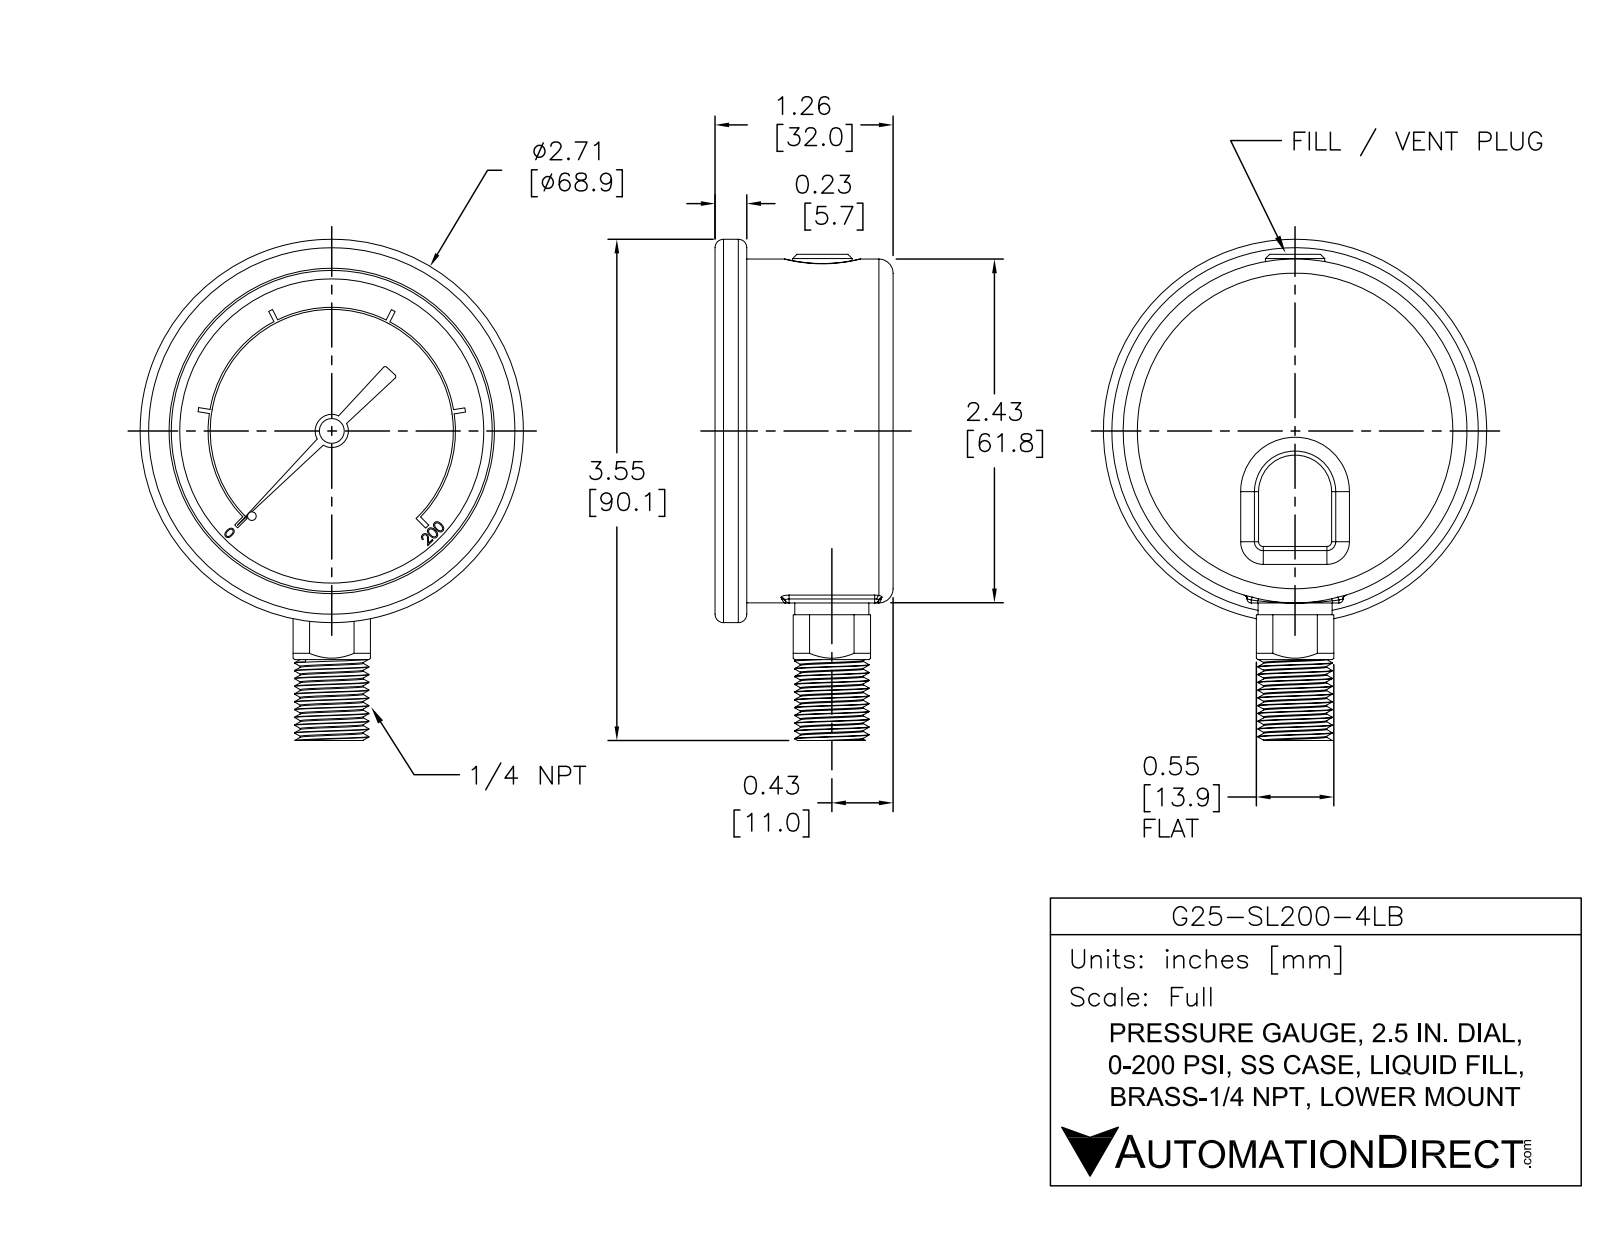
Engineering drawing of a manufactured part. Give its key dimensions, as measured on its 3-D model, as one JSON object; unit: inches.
{"part_name": "G25-SL200-4LB", "step_written_by": "SolidWorks 2021 (AUTOMOTIVE_DESIGN)", "units": "inches", "bodies": {"solids": 1, "faces": 349, "planar": 195, "cylindrical": 85, "other": 69}, "overall_size": [3.546, 2.713, 1.26], "volume_in3": 5.273, "surface_area_in2": 24.68, "round_holes": [[0.027, 1], [0.071, 1], [0.119, 1], [2.272, 1]], "round_bosses_or_shafts": [[2.713, 1], [2.433, 1], [0.524, 1], [0.42, 1], [0.235, 1], [0.176, 1], [0.14, 1], [0.041, 1]], "partial_cylinders_radius": [[0.03, 9], [0.1, 3], [0.015, 2], [0.316, 1], [0.86, 1], [0.875, 1]], "face_to_face_distances": [1.01, 1.26, 0.25, 1.035, 0.025, 0.225, 0.1, 0.91, 0.935, 1.16], "hole_center_spacings": [0.067]}
